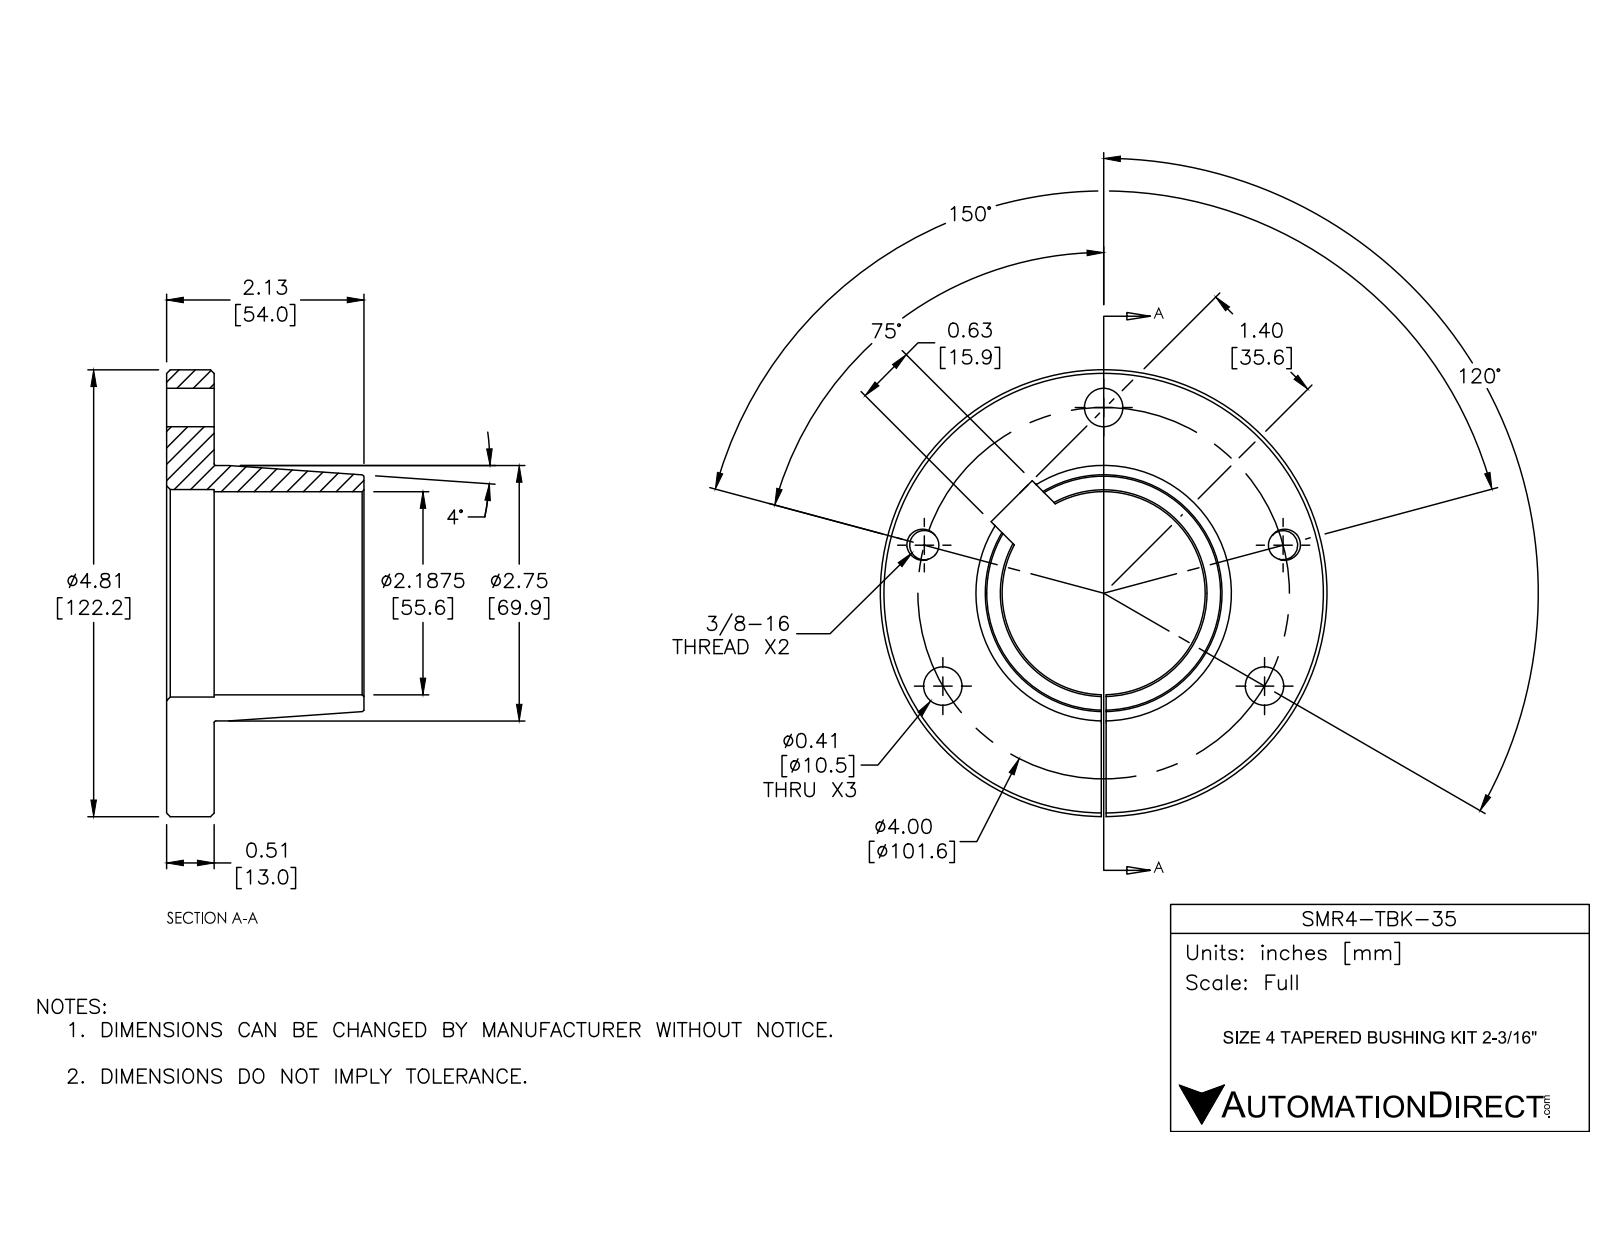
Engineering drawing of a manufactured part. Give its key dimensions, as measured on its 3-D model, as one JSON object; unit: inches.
{"part_name": "SMR4-TBK-35", "step_written_by": "SolidWorks 2016 (AUTOMOTIVE_DESIGN)", "units": "inches", "bodies": {"solids": 1, "faces": 128, "planar": 11, "cylindrical": 92, "other": 25}, "overall_size": [4.811, 4.811, 2.126], "volume_in3": 9.475, "surface_area_in2": 65.88, "round_holes": [[0.413, 3], [0.315, 2], [0.375, 2], [2.187, 1], [2.235, 1]], "round_bosses_or_shafts": [[4.811, 1], [2.75, 1]], "face_to_face_distances": [0.512, 0.051, 2.126, 1.614, 0.625], "hole_center_spacings": [2, 1.531, 2.435, 3.464, 3.966, 3.464, 3.864]}
